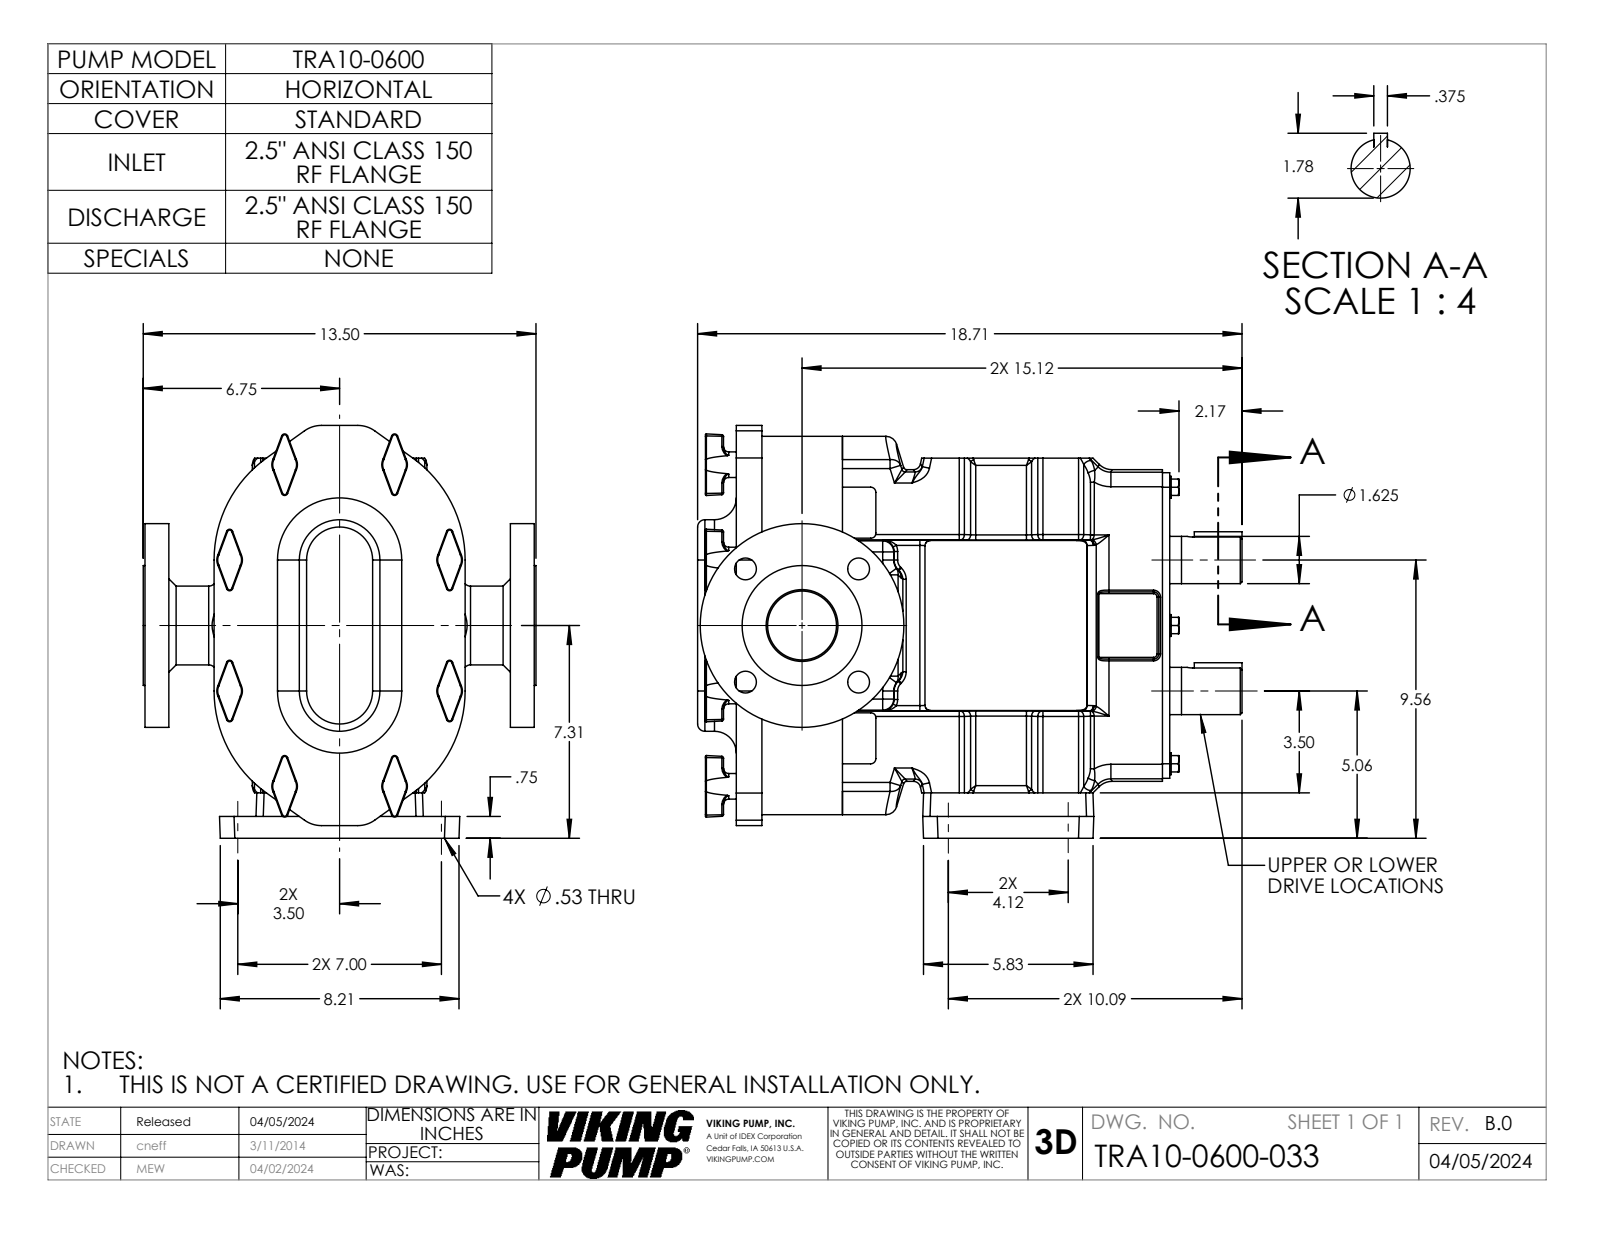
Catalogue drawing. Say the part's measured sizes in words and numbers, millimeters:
The part is named "TRA10-0600-033; TRA10-0600-COVER-STD; 0600FLG150-25; TRA10-0600-BODY (+1 more)". Its 3-D file was written by "SolidWorks 2022 (AUTOMOTIVE_DESIGN)". It is 5 solids with 1059 faces: 287 planar, 392 cylindrical and 380 other. Overall it measures 475.3 by 360.3 by 342.9 millimeters. Its volume is 20 320 000 cubic millimeters and its surface area 989 700 square millimeters. Round holes: 4 of diameter 13.5, 4 of diameter 19.1, 1 of diameter 60.1, 1 of diameter 62.7. Round bosses or shafts: 8 of diameter 22.4, 6 of diameter 19.1, 2 of diameter 41.2, 1 of diameter 177.8, 1 of diameter 104.6, 1 of diameter 68.8. Partial cylindrical surfaces (rounded edges, fillets, slot ends): 44 of radius 4.6, 43 of radius 1.5, 32 of radius 0.8, 32 of radius 6.4, 28 of radius 9.7, 24 of radius 3, 20 of radius 12.7, 12 of radius 9.5. The main face-to-face distances are 70.3, 22.4, 12.7, 92.7, 285.8, 9.1, 60.2, 238, 378.4, 356.1. The hole center spacings are 69.9, 98.8, 104.6, 139.7, 177.8, 206.3.
